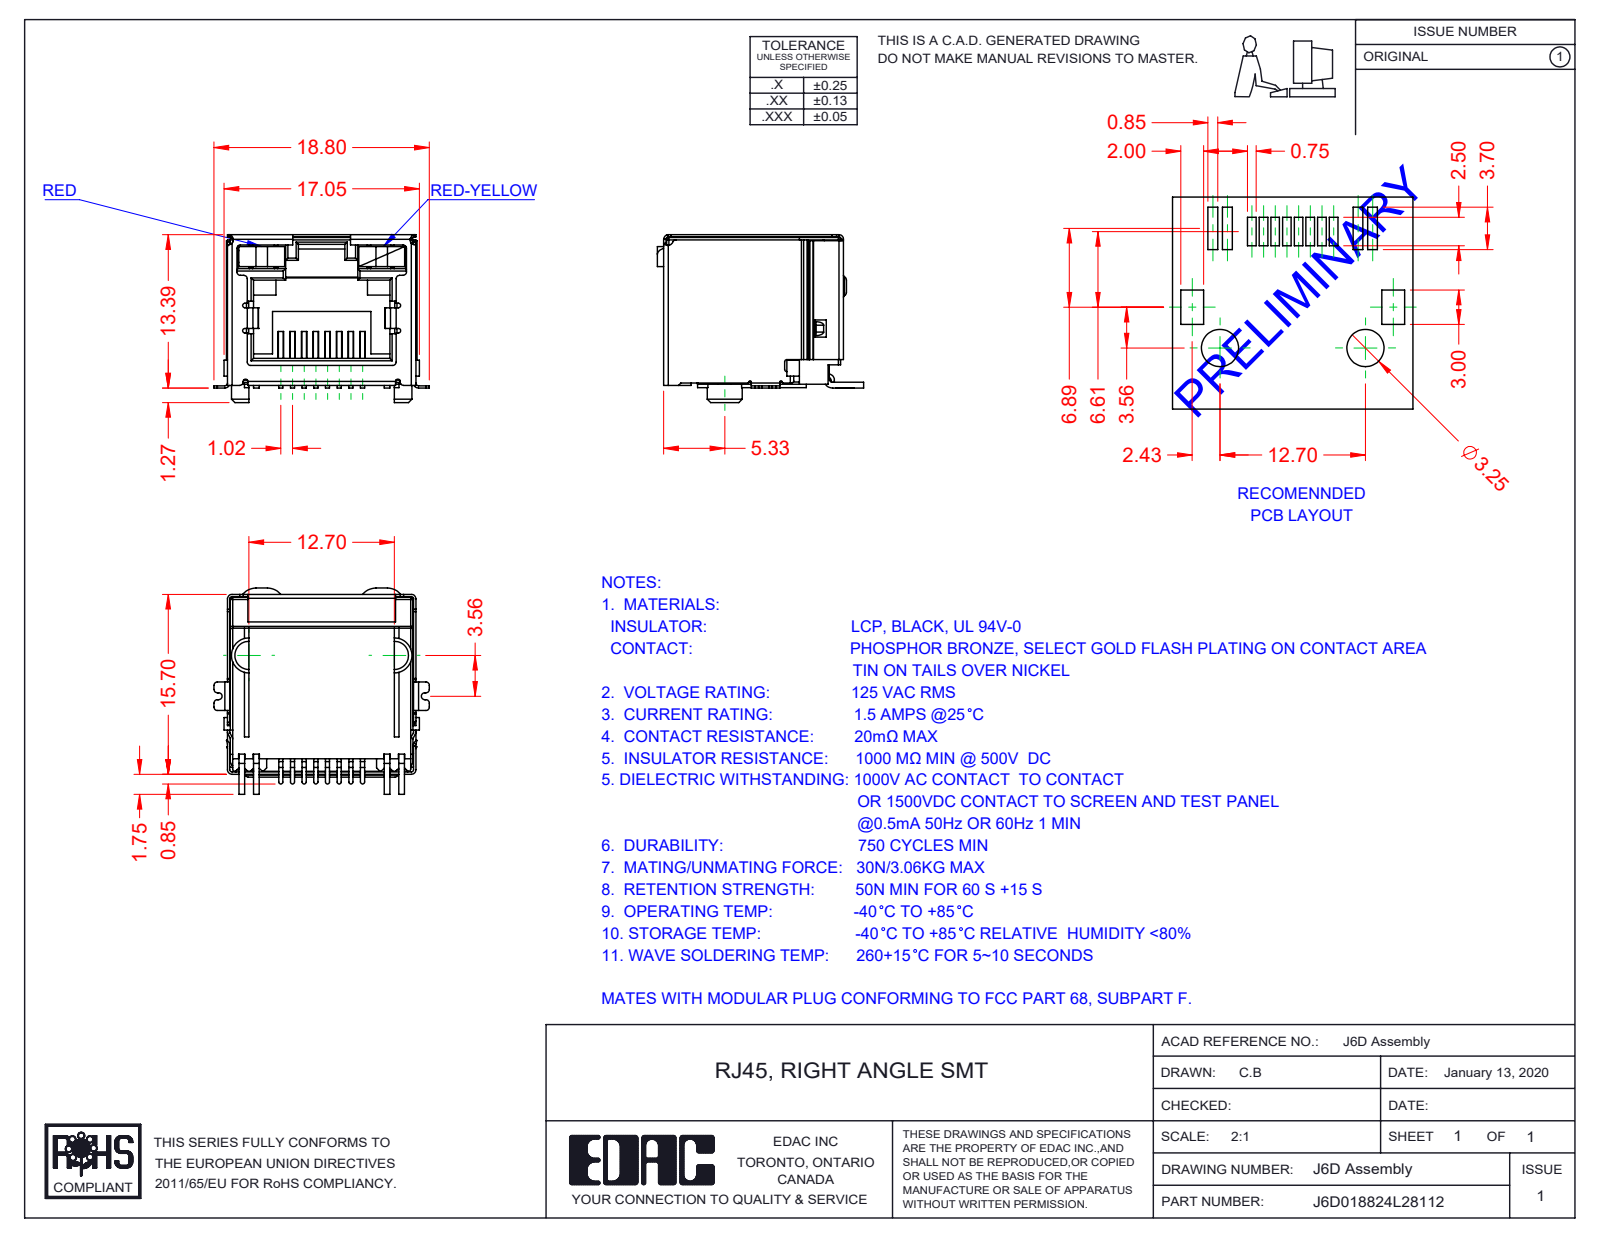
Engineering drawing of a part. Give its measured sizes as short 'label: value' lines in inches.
name: 6D LED LH_2-Red; 6D Contacts; 6D Insulator; 6D Shield_LED - No EMI (+2 more)
written by: SolidWorks 2016 (CONFIG_CONTROL_DESIGN)
unit: in
bodies: 12 solids, 896 faces (645 planar, 218 cylindrical, 33 other)
size: 0.74 × 0.709 × 0.577
volume: 0.11 in³; area: 7.592 in²
rounds: 39× R0.012, 37× R0.008, 16× R0.016, 12× R0.004, 8× R0.006, 8× R0.007, 6× R0.02, 5× R0.059
face distances: 0.63, 0.64, 0.638, 0.089, 0.039, 0.628, 0.632, 0.504, 0.018, 0.648
